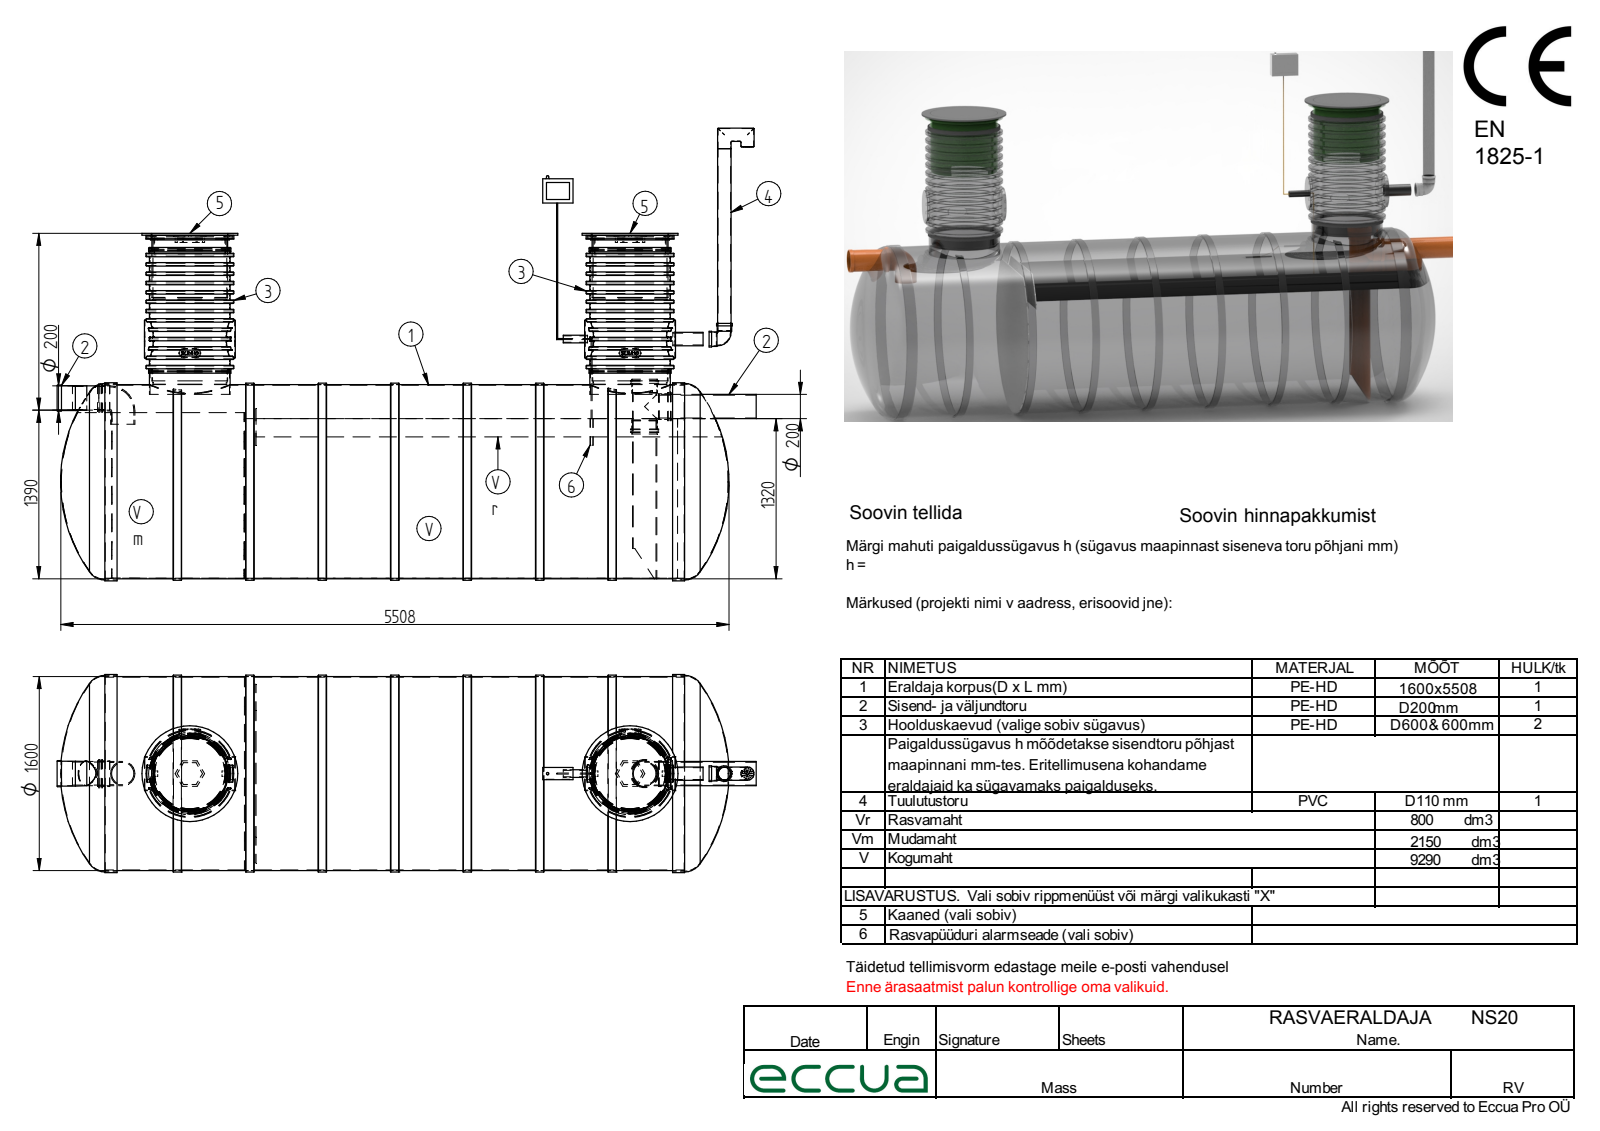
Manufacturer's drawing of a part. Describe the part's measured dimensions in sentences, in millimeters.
The part is named "Rasvaeraldaja NS20; 2261.013; Silinder D1600 rasvaeraldaja NS20; 2261.014 (+8 more)". Its 3-D file was written by "Solid Edge (AUTOMOTIVE_DESIGN)". It is 50 solids with 1259 faces: 486 planar, 392 cylindrical and 381 other. Overall it measures 5764 by 4192.01 by 2555.02 millimeters. Its volume is 10 370 000 000 cubic millimeters and its surface area 231 800 000 square millimeters. Round holes: 31 of diameter 10, 4 of diameter 200, 3 of diameter 103.2, 2 of diameter 6, 2 of diameter 100, 2 of diameter 188, 2 of diameter 220, 2 of diameter 595, 2 of diameter 600, 2 of diameter 609, 2 of diameter 615, 2 of diameter 630. Round bosses or shafts: 4 of diameter 110, 3 of diameter 212, 3 of diameter 8.5, 2 of diameter 790, 2 of diameter 725, 2 of diameter 678.5, 2 of diameter 665, 2 of diameter 650. Partial cylindrical surfaces (rounded edges, fillets, slot ends): 8 of radius 5, 8 of radius 30, 8 of radius 35, 6 of radius 3, 2 of radius 135, 2 of radius 140, 2 of radius 289.9, 1 of radius 130. The main face-to-face distances are 150, 8, 5, 50, 200, 1126, 88, 1678, 1528, 1478. The hole center spacings are 40, 49.88, 62.55, 72.08, 26.75, 34.71, 78, 13.5.
